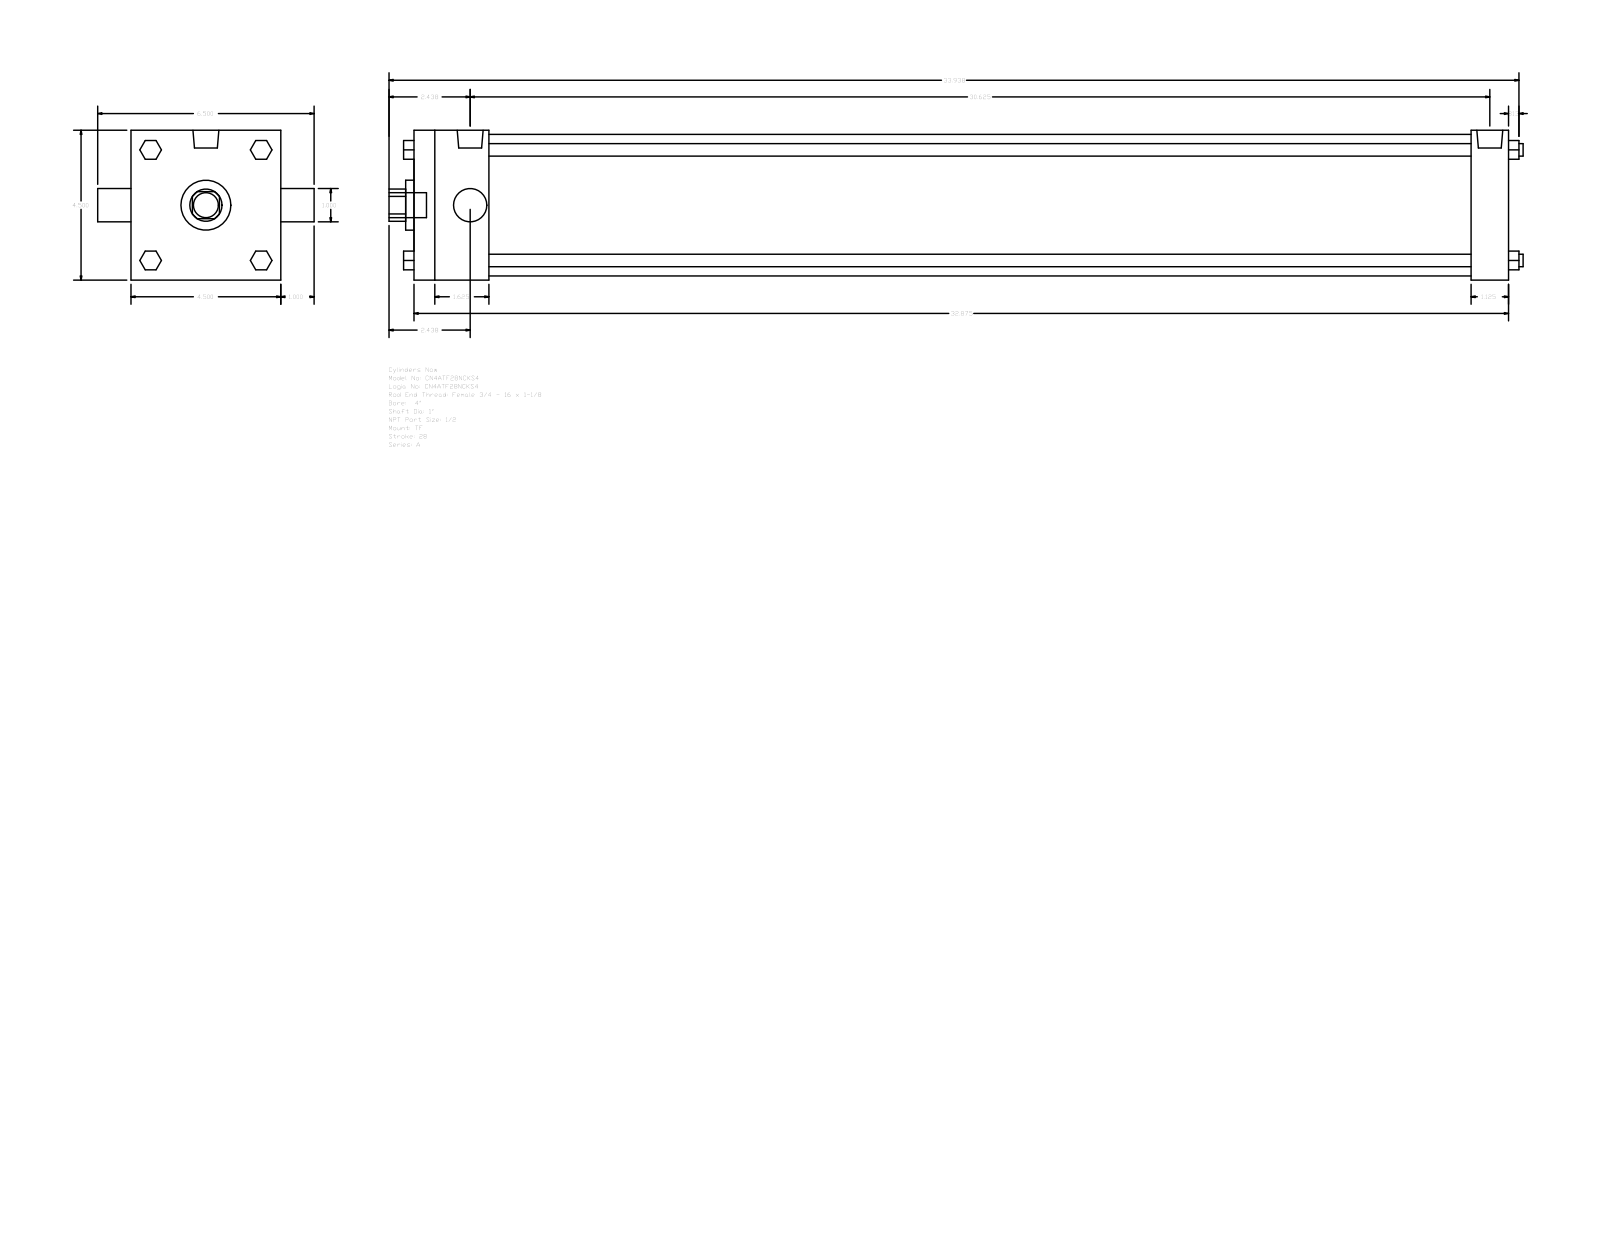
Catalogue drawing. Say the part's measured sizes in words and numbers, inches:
The part is named "A_TF__0400_1". Its 3-D file was written by "GSSL Pune (CONFIG_CONTROL_DESIGN)". It is 0 solids with 120 faces: 92 planar, 28 cylindrical and 0 other. Overall it measures 34.063 by 6.5 by 4.5 inches. Round holes: 2 of diameter 1, 1 of diameter 1.5, 1 of diameter 4.25. Round bosses or shafts: 4 of diameter 0.375, 3 of diameter 0.344, 2 of diameter 0.778, 1 of diameter 0.75. Partial cylindrical surfaces (rounded edges, fillets, slot ends): 1 of radius 0.484. The main face-to-face distances are 4.5, 32.875, 31.75, 1.125, 2.25, 29.5, 30.625, 0.563, 1.66, 2.875.
